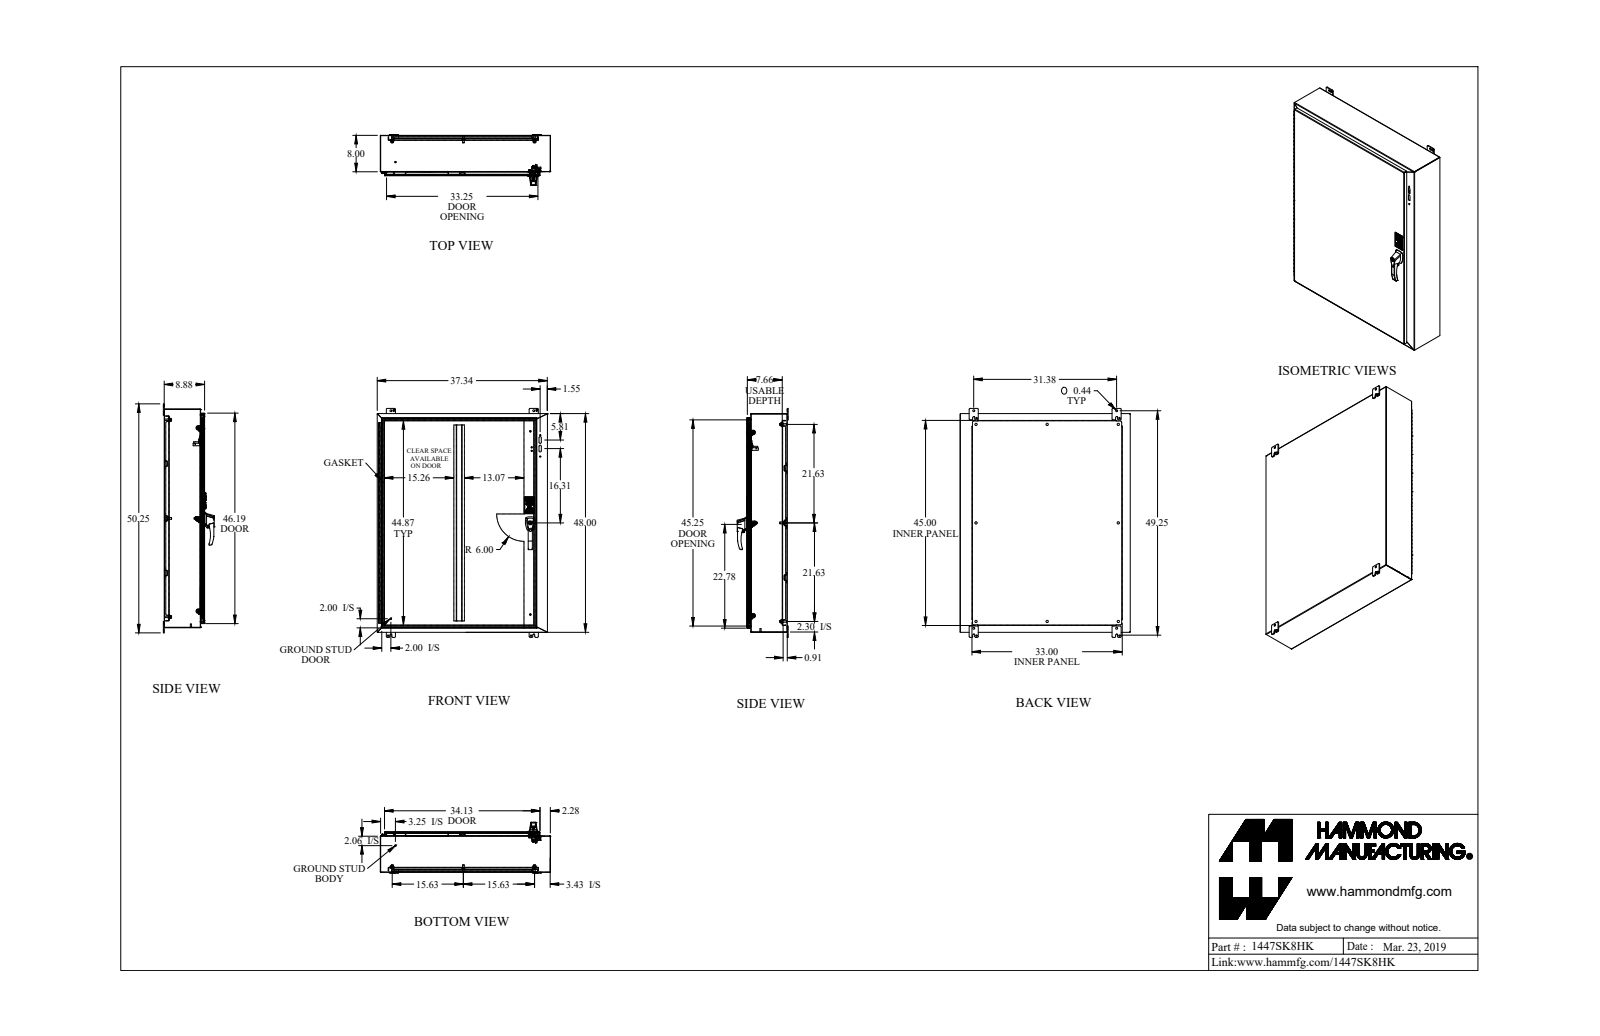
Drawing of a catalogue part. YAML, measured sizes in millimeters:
part_name: "1447SK8HK"
step_written_by: "SolidWorks 2019 (AUTOMOTIVE_DESIGN)"
units: millimeters
bodies: {solids: 69, faces: 1615, planar: 995, cylindrical: 480, other: 140}
overall_size: [1276.34, 949.33, 283.9]
volume: 9891000
surface_area: 9918000
round_holes:
  - {diameter: 12.7, count: 8}
  - {diameter: 4.47, count: 6}
  - {diameter: 7.94, count: 6}
  - {diameter: 7.81, count: 4}
  - {diameter: 11.11, count: 4}
  - {diameter: 11.3, count: 4}
  - {diameter: 6.35, count: 3}
  - {diameter: 6.73, count: 3}
  - {diameter: 10.49, count: 3}
  - {diameter: 3.97, count: 2}
  - {diameter: 4.39, count: 2}
  - {diameter: 4.98, count: 2}
round_bosses_or_shafts:
  - {diameter: 9.53, count: 13}
  - {diameter: 6.35, count: 9}
  - {diameter: 16.51, count: 8}
  - {diameter: 8.38, count: 8}
  - {diameter: 25.4, count: 7}
  - {diameter: 3.97, count: 6}
  - {diameter: 16, count: 2}
  - {diameter: 12.95, count: 2}
partial_cylinders:
  - {radius: 4.76, count: 36}
  - {radius: 2, count: 28}
  - {radius: 6.35, count: 21}
  - {radius: 0.17, count: 16}
  - {radius: 2.93, count: 16}
  - {radius: 3.17, count: 16}
  - {radius: 0.76, count: 10}
  - {radius: 3.83, count: 8}
face_to_face_distances: [1.83, 223.6, 221.77, 225.43, 2.41, 197.39, 195.56, 26.21, 28.04, 199.8]
hole_center_spacings: [965.27, 793.75, 796.93, 1168.04, 28.21, 396.88, 549.27, 677.65]
